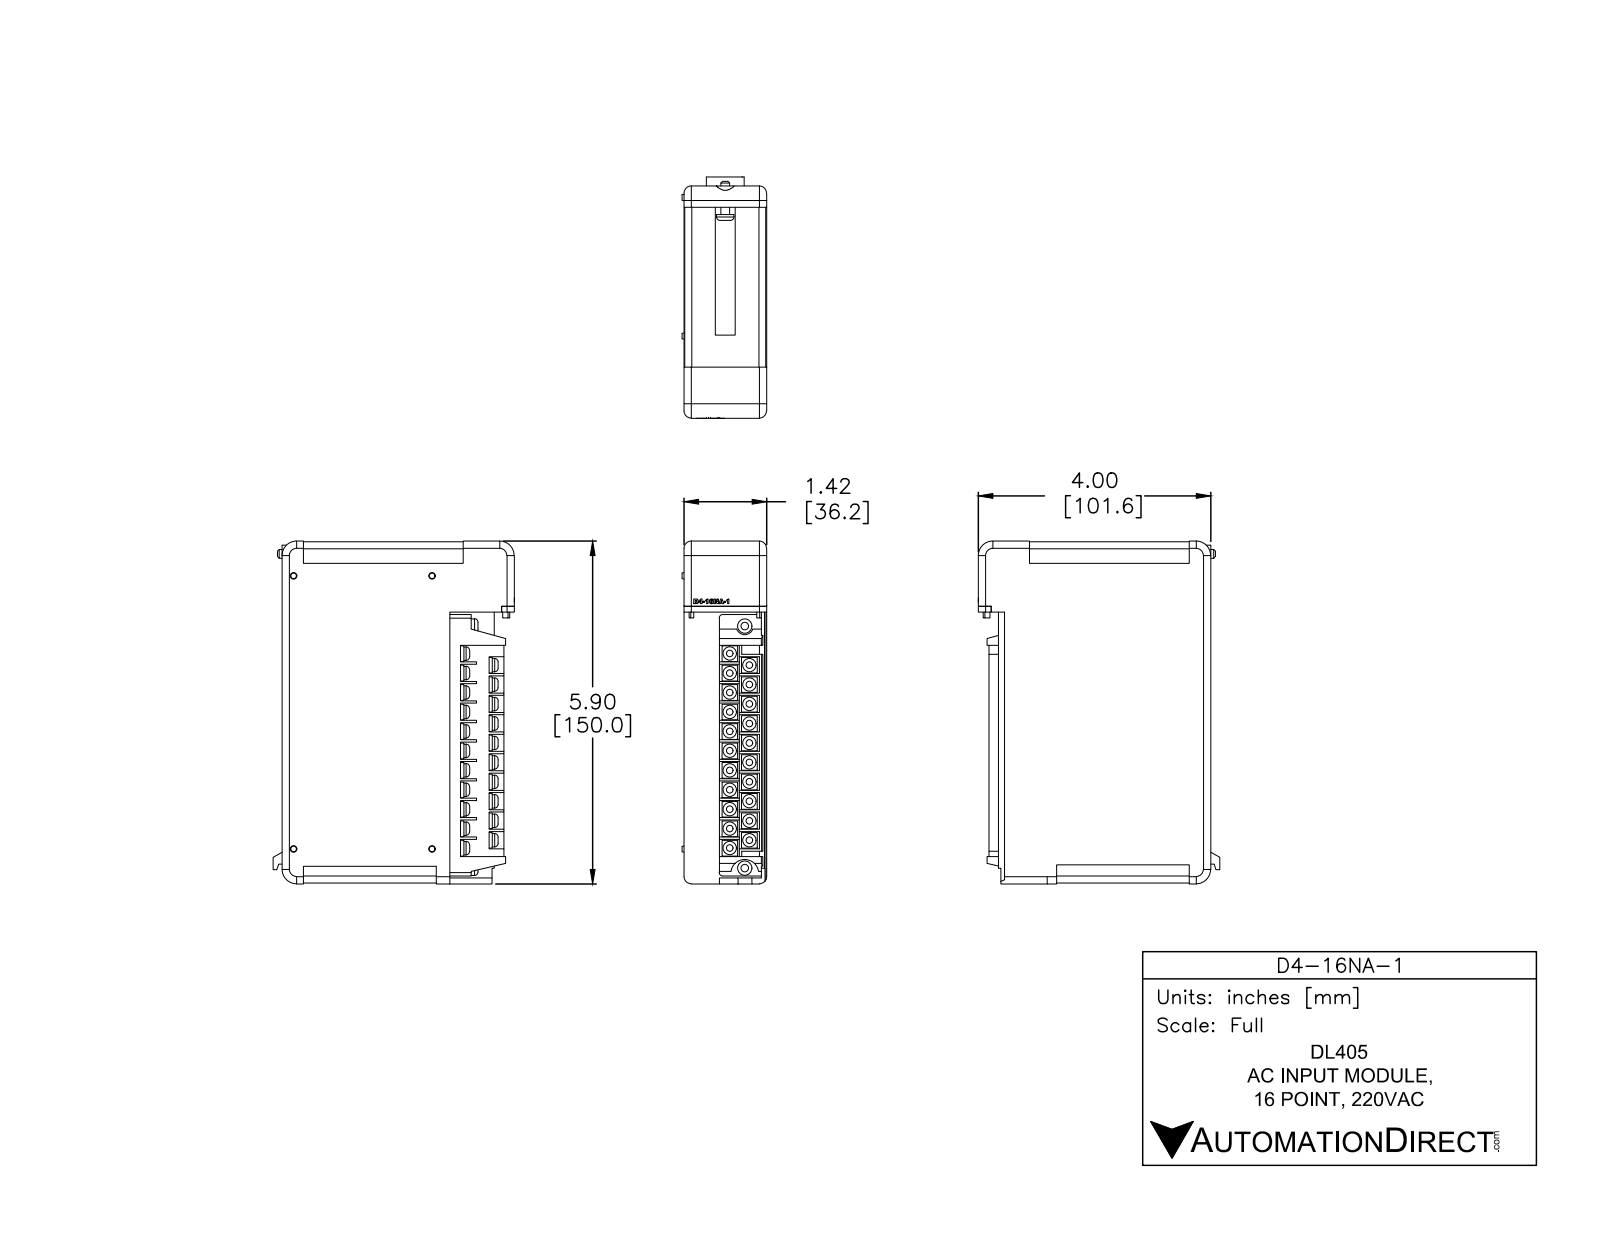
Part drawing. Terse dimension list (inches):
name: D4-16NA-1
written by: SolidWorks 2014 (AUTOMOTIVE_DESIGN)
unit: in
bodies: 15 solids, 600 faces (426 planar, 86 cylindrical, 88 other)
size: 5.905 × 4.156 × 1.455
volume: 27.51 in³; area: 86.82 in²
bosses: 21× ⌀0.23, 2× ⌀0.25, 1× ⌀0.3, 1× ⌀0.15
rounds: 8× R0.125, 4× R0.12, 3× R0.25, 2× R0.015, 2× R0.03, 2× R0.06, 1× R0.149, 1× R0.151
face distances: 1.425, 0.015, 2.89, 5.875, 1.41, 0.47, 0.2, 0.955, 5.89, 1.21
